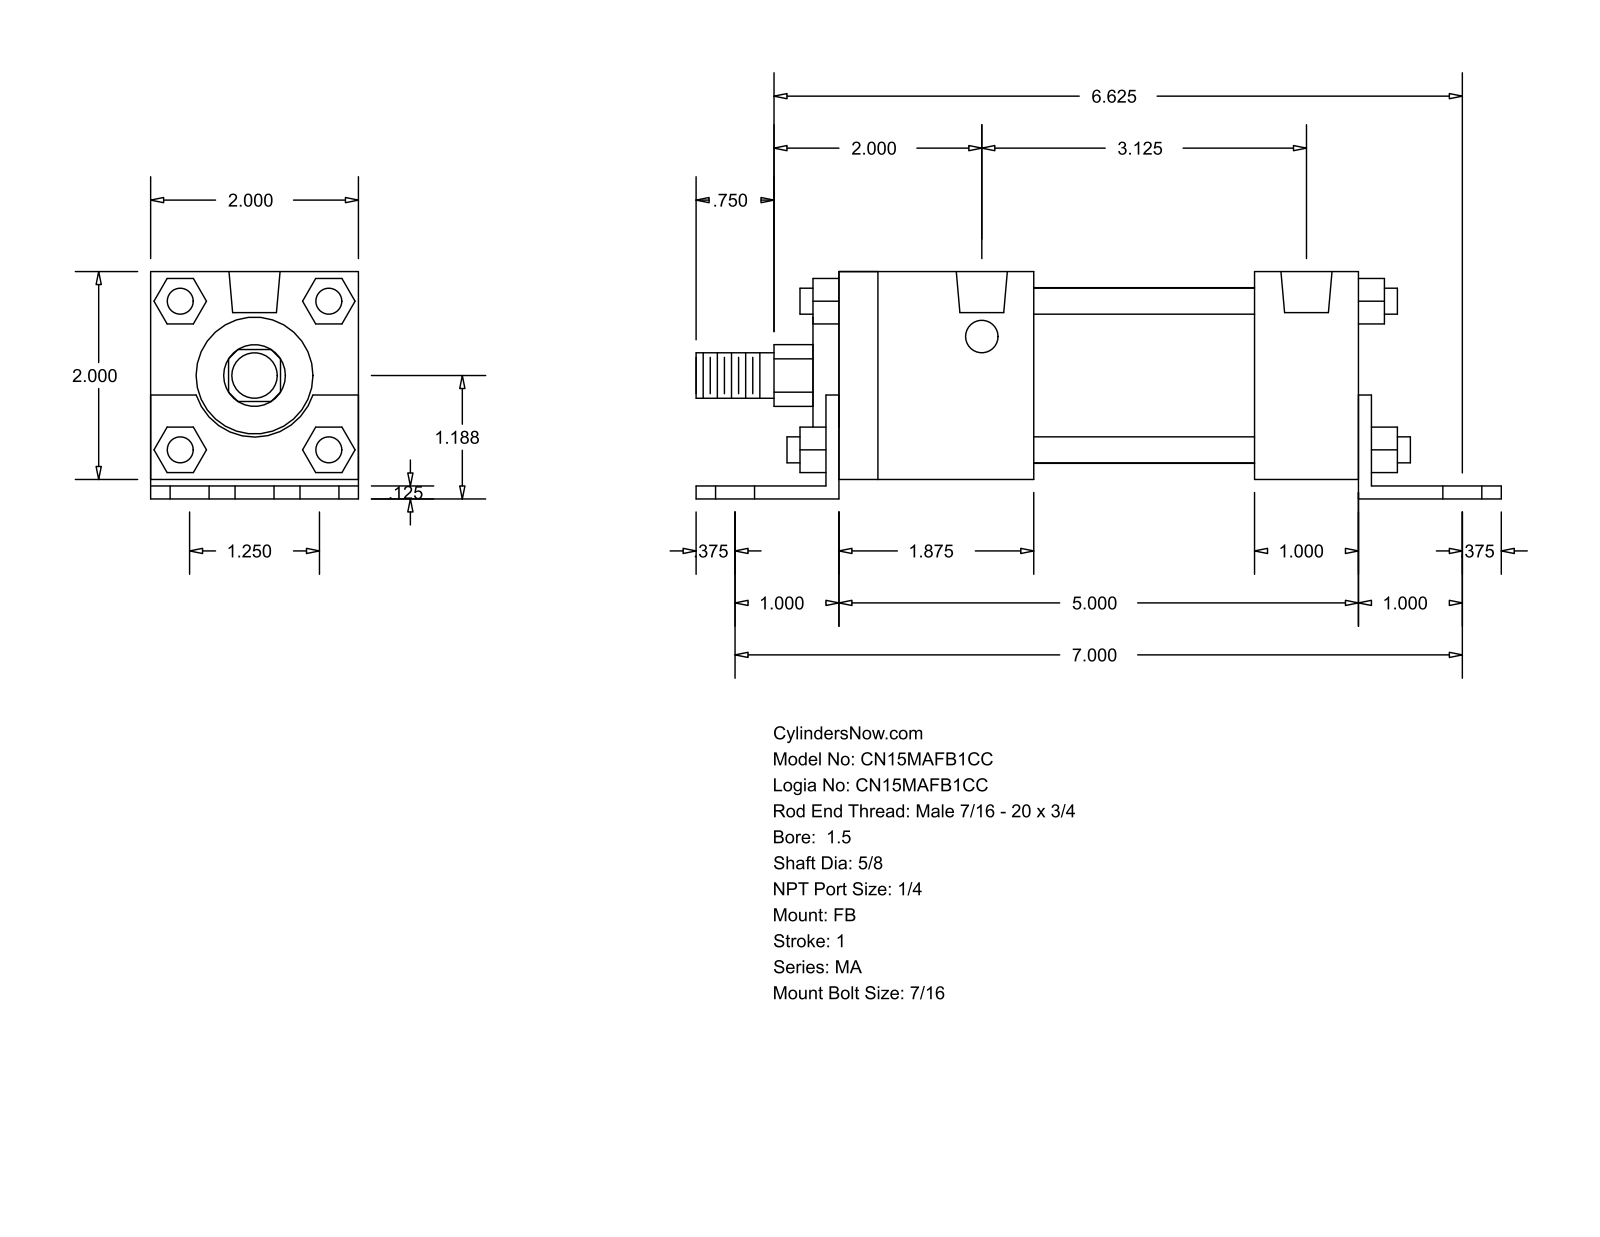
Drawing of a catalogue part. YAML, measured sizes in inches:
part_name: "MA_FB__0150_0.625"
step_written_by: "GSSL Pune (CONFIG_CONTROL_DESIGN)"
units: inches
bodies: {solids: 0, faces: 140, planar: 105, cylindrical: 35, other: 0}
overall_size: [7.75, 2.187, 2]
round_holes:
  - {diameter: 0.437, count: 6}
  - {diameter: 0.313, count: 4}
  - {diameter: 0.492, count: 2}
round_bosses_or_shafts:
  - {diameter: 0.25, count: 4}
  - {diameter: 1.69, count: 1}
  - {diameter: 1.125, count: 1}
  - {diameter: 0.625, count: 1}
  - {diameter: 0.437, count: 1}
partial_cylinders:
  - {radius: 0.297, count: 1}
  - {radius: 0.593, count: 1}
face_to_face_distances: [2, 0.125, 0.187, 2.187, 0.063, 2.063, 2.125, 1.125, 5.25, 5.375]
hole_center_spacings: [0.625, 7.028, 7, 1.25, 1.625, 2.456, 3.125, 4.667]
